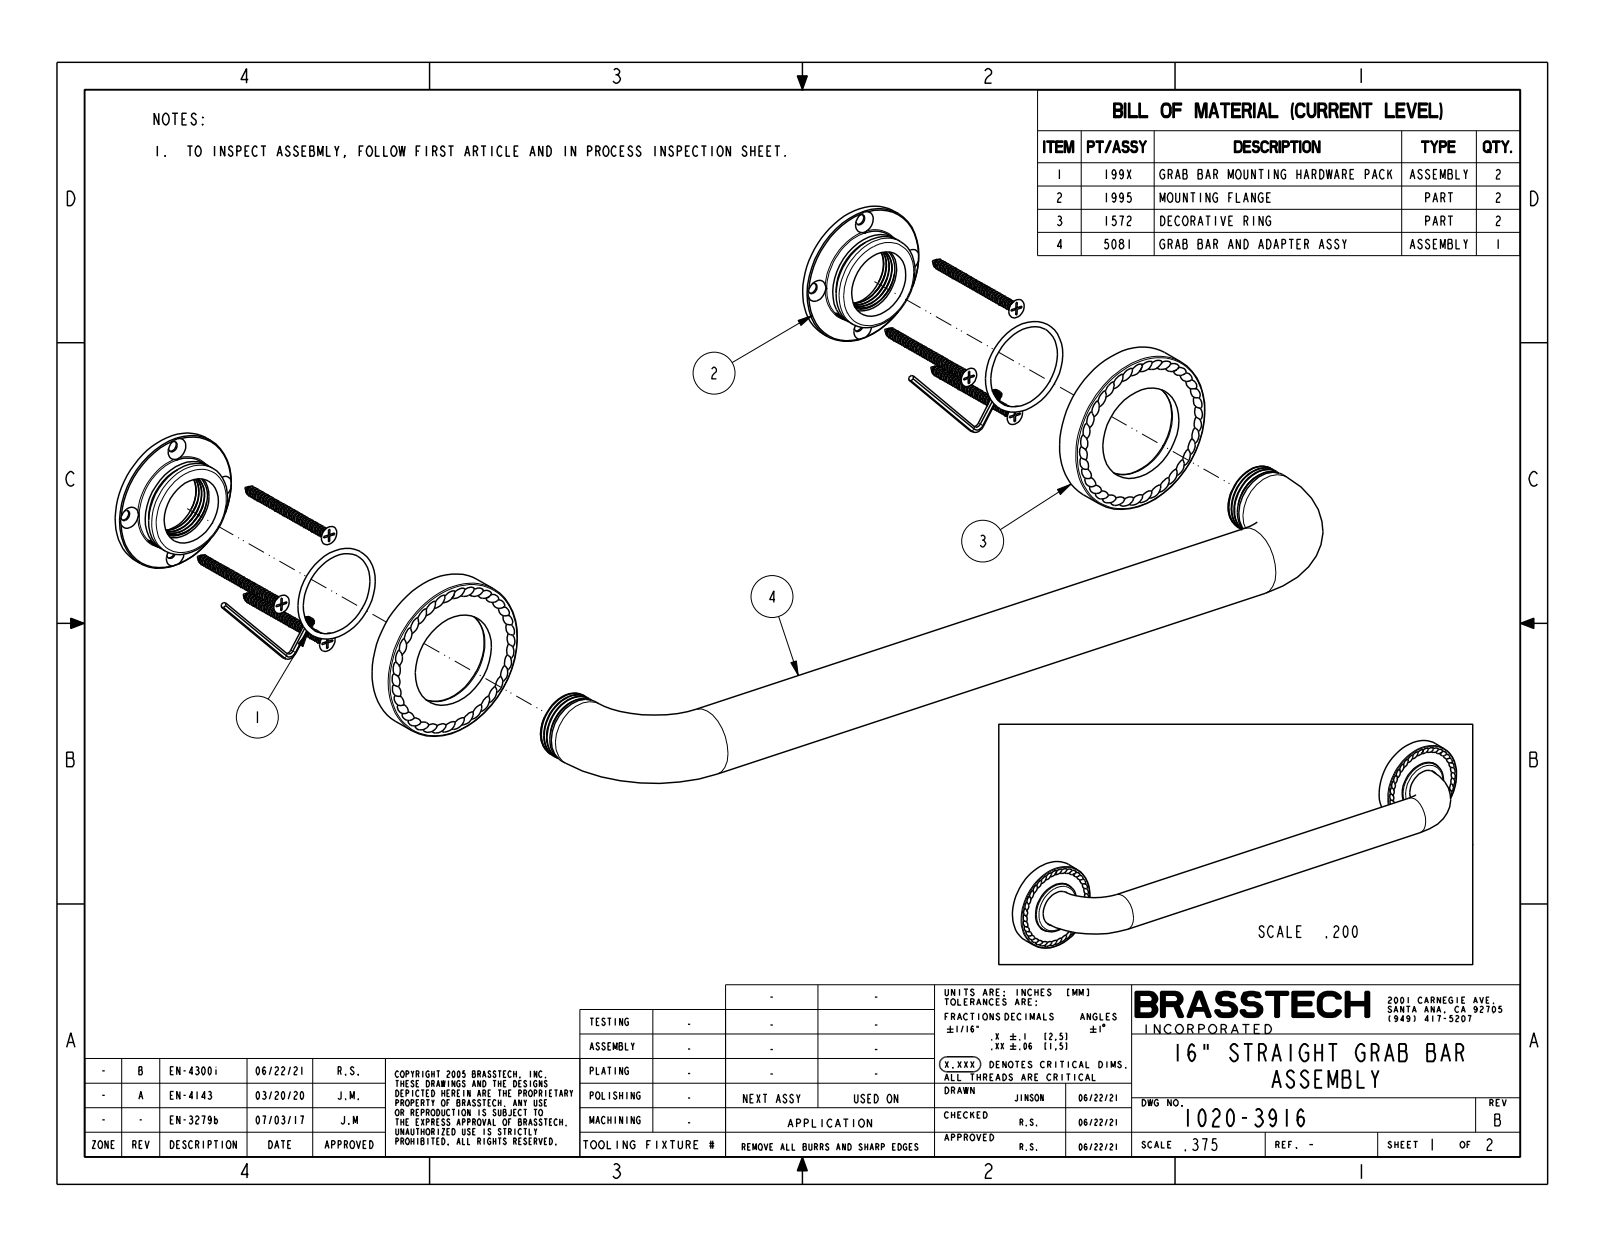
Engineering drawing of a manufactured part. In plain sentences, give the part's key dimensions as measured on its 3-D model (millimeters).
The part is named "1020-3916". Its 3-D file was written by "CREO PARAMETRIC BY PTC INC, 2018400 (CONFIG_CONTROL_DESIGN)". It is 1 solid with 106 faces: 8 planar, 10 cylindrical and 88 other. Overall it measures 482.6 by 76.2 by 69.9 millimeters. Its volume is 480 100 cubic millimeters and its surface area 68 450 square millimeters. Round bosses or shafts: 2 of diameter 76.2, 2 of diameter 44.5, 1 of diameter 31.8. The main face-to-face distances are 12.7, 15.2, 2.5.
